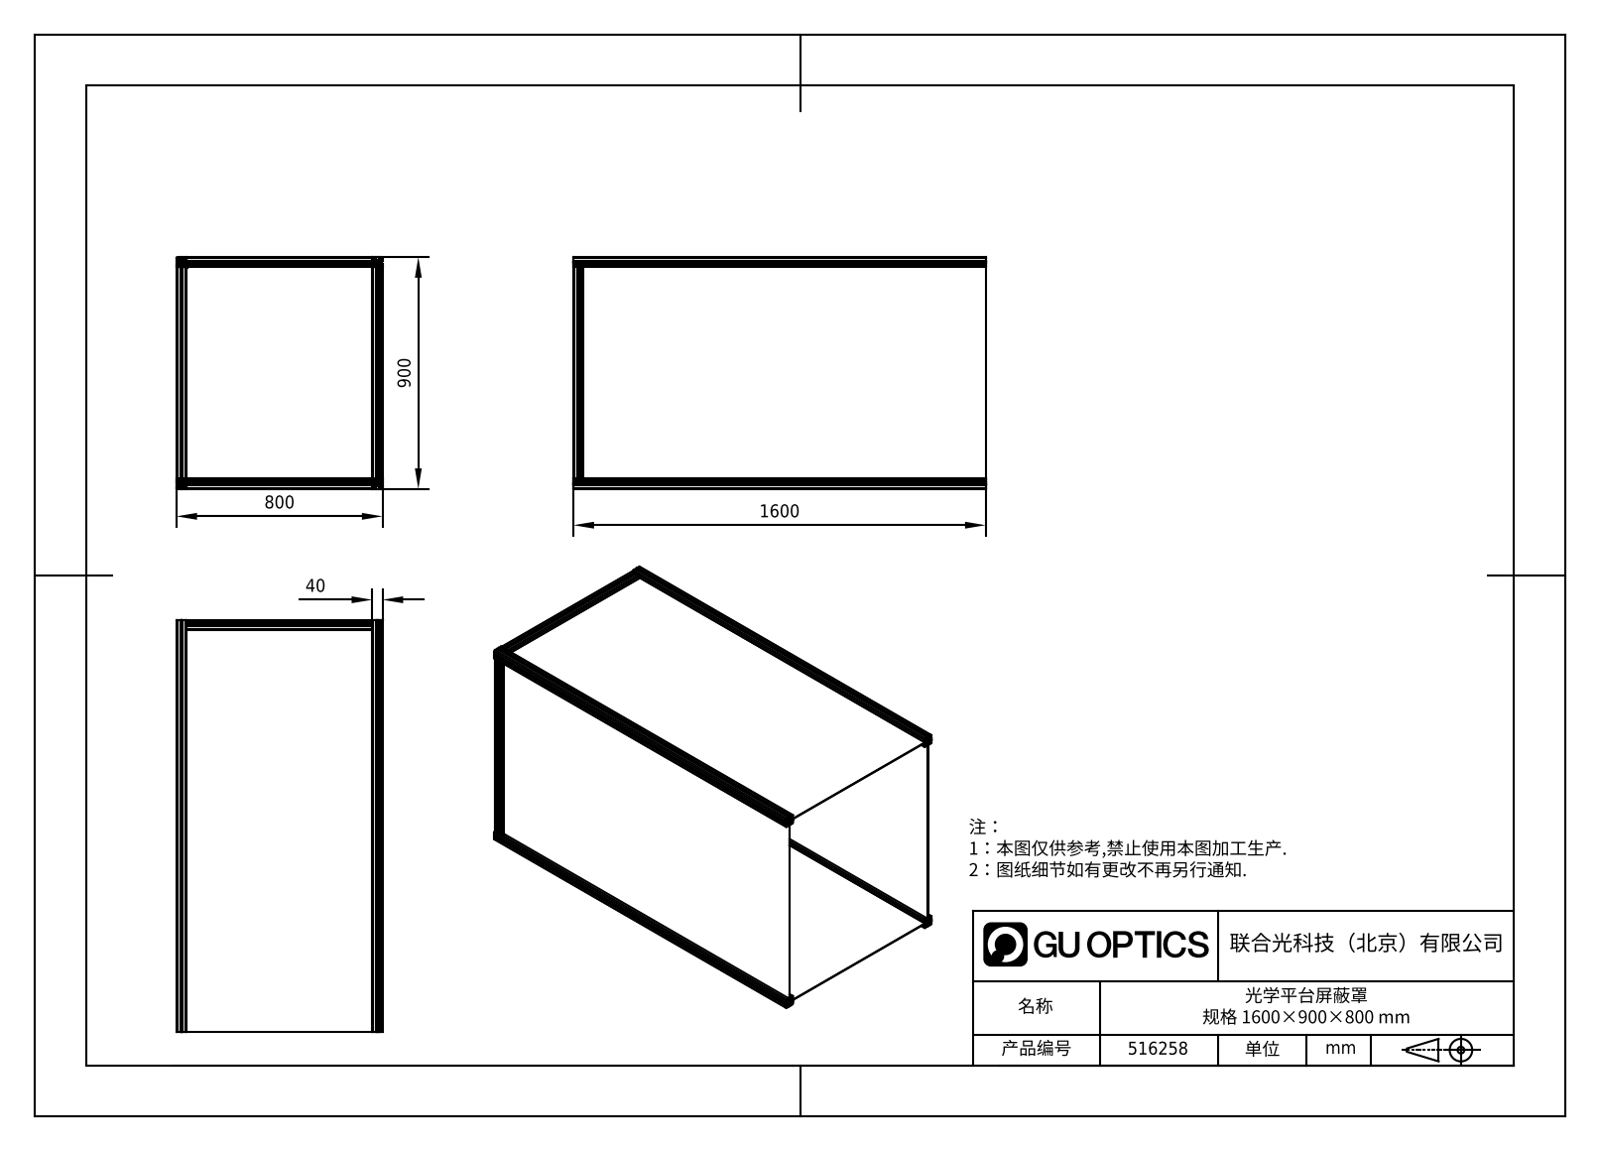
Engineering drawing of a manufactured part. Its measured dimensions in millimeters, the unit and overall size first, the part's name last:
Units: millimetres
Overall size (bounding box): 1600 × 900 × 800
Partial cylindrical surfaces — rounded edges, fillets, slot ends (radius × count): R0.5 ×64, R1 ×64, R0.75 ×32, R2.5 ×32, R4.5 ×32, R3.4 ×8
Main face-to-face distances: 2, 760, 860, 762, 758, 862, 858, 19, 21, 8.2
Volume: 16 920 000 mm³ · Surface area: 15 960 000 mm²
Bodies: 13 solids, 1230 faces (950 planar, 280 cylindrical, 0 other)
Part name (STEP PRODUCT): 516258; 光学平台屏蔽罩边框_720; 光学平台屏蔽罩面板_844_1572; 光学平台屏蔽罩面板_744_1572 (+3 more)
STEP written by: SolidWorks 2020 (CONFIG_CONTROL_DESIGN)
